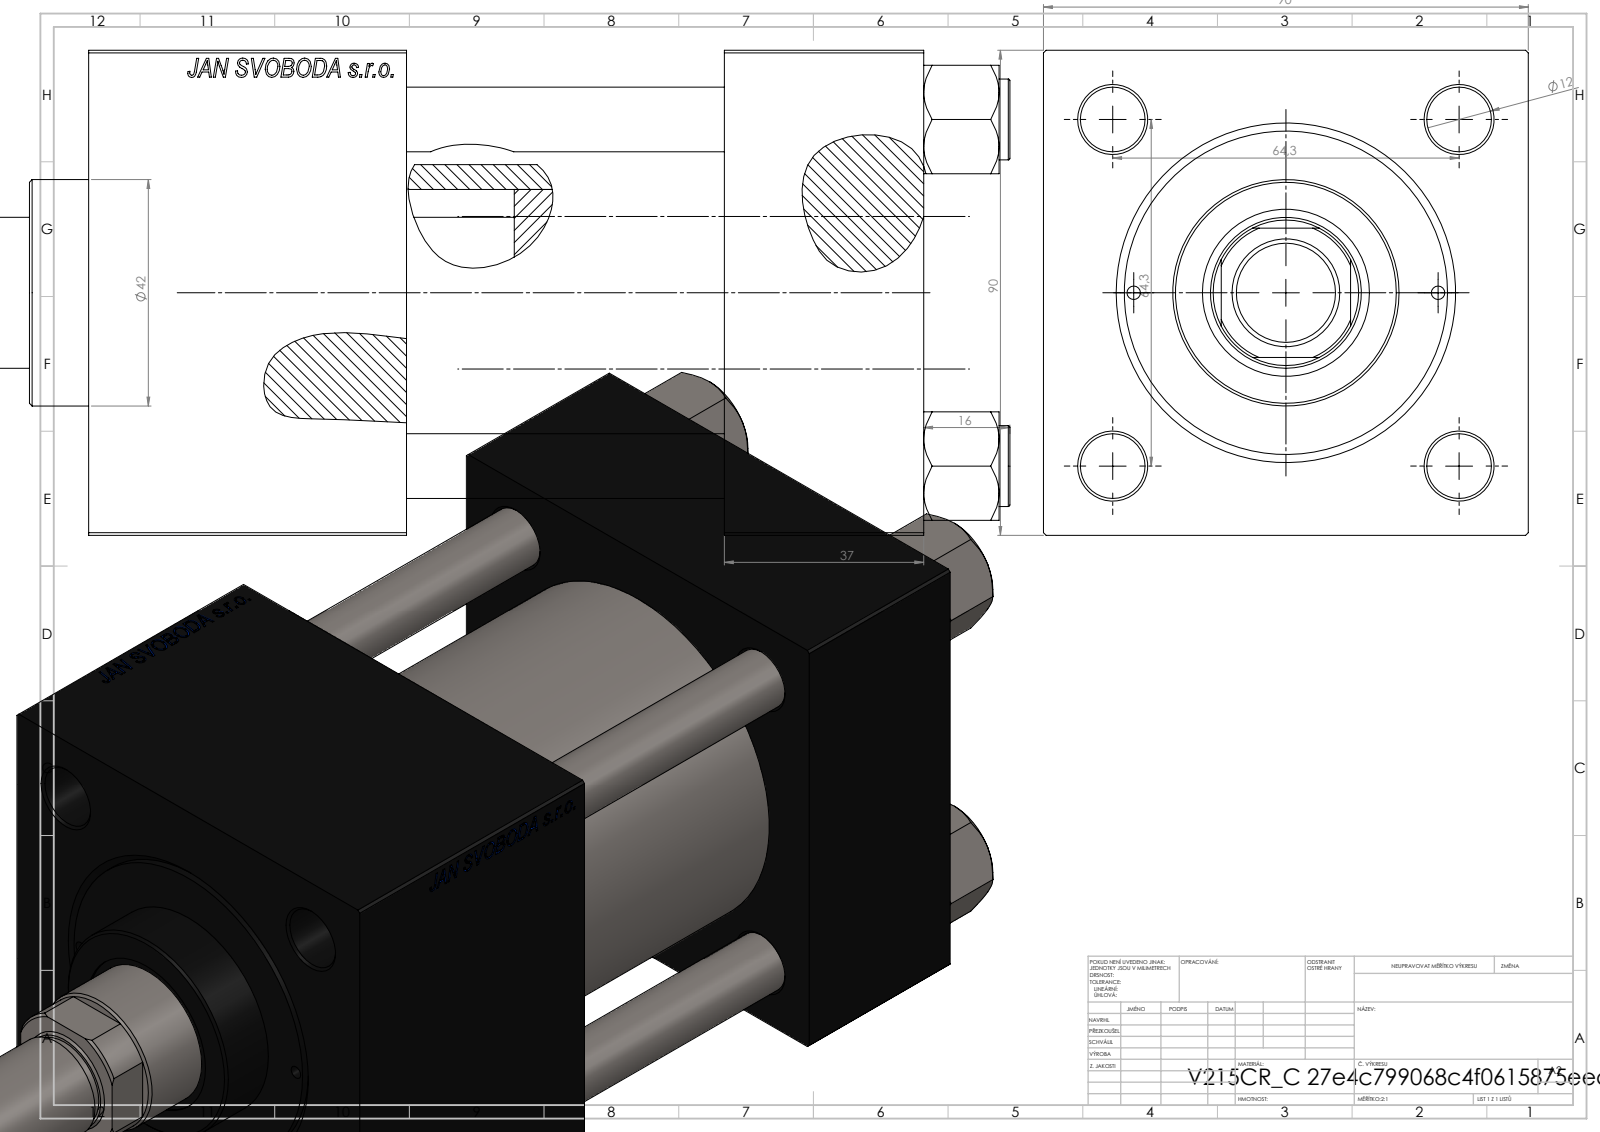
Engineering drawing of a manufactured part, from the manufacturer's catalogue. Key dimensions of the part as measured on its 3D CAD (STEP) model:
Part name (STEP PRODUCT): V215CR_VCP_C; V215_VC_A; V215CR_C_TYCINKA; V215CR_C_Body (+2 more)
STEP written by: SolidWorks 2019 (CONFIG_CONTROL_DESIGN)
Units: millimetres
Bodies: 12 solids, 1168 faces (532 planar, 94 cylindrical, 542 other)
Overall size (bounding box): 231 × 90 × 90
Volume: 955 489 mm³ · Surface area: 181 640 mm²
Round holes (diameter × count): ⌀12 ×4, ⌀2.5 ×2, ⌀7 ×2, ⌀20.96 ×2, ⌀30 ×2, ⌀18.5 ×1, ⌀28 ×1, ⌀31 ×1, ⌀50 ×1, ⌀60 ×1, ⌀63 ×1
Round bosses / shafts (diameter × count): ⌀15 ×4, ⌀69 ×1, ⌀42 ×1, ⌀20 ×1, ⌀18 ×1
Partial cylindrical surfaces — rounded edges, fillets, slot ends (radius × count): R13.5 ×1
Main face-to-face distances: 90, 59, 37, 155, 118, 96, 126.3, 89.3, 30.3, 28.7
Hole centre spacings: 32.39, 45.47, 64.3, 68.42, 28.25, 90.93, 56.5, 97.5
